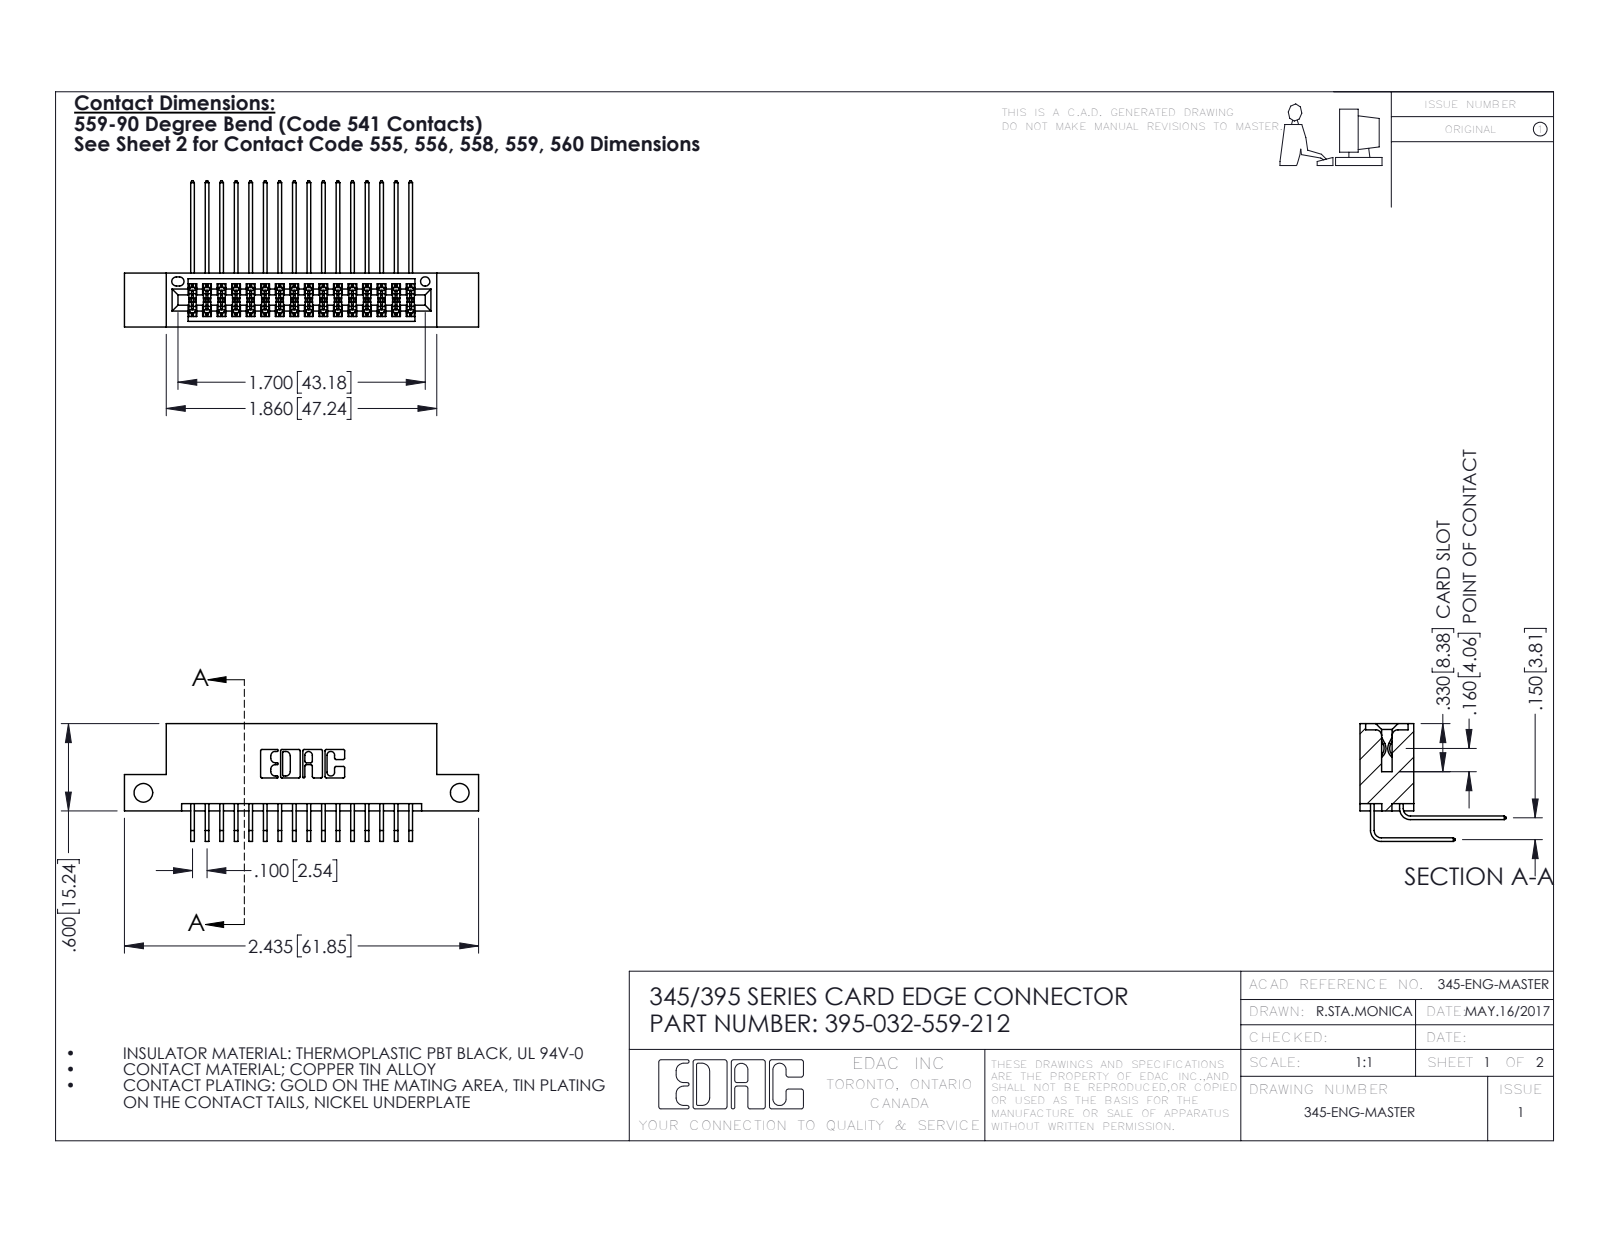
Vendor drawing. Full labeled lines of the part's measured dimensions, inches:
Part name (STEP PRODUCT): 345 Part_Flush Mounting Lugs - Side Mount; 395-032-559-212; 345-292-001_558 559 Tail - 1; 345-292-001_559 Tail - 2
STEP written by: SolidWorks 2016 (CONFIG_CONTROL_DESIGN)
Units: inches
Bodies: 33 solids, 1790 faces (1200 planar, 590 cylindrical, 0 other)
Overall size (bounding box): 2.435 × 1.005 × 0.809
Volume: 0.358 in³ · Surface area: 13.79 in²
Round holes (diameter × count): ⌀0.128 ×2, ⌀0.064 ×1
Partial cylindrical surfaces — rounded edges, fillets, slot ends (radius × count): R0.006 ×49, R0.01 ×22, R0.007 ×6, R0.031 ×6, R0.026 ×3, R0.014 ×2, R0.019 ×2, R0.022 ×2
Main face-to-face distances: 0.072, 0.298, 0.2, 0.37, 0.098, 0.272, 0.025, 0.225, 0.15, 0.175
Hole centre spacings: 2.175
